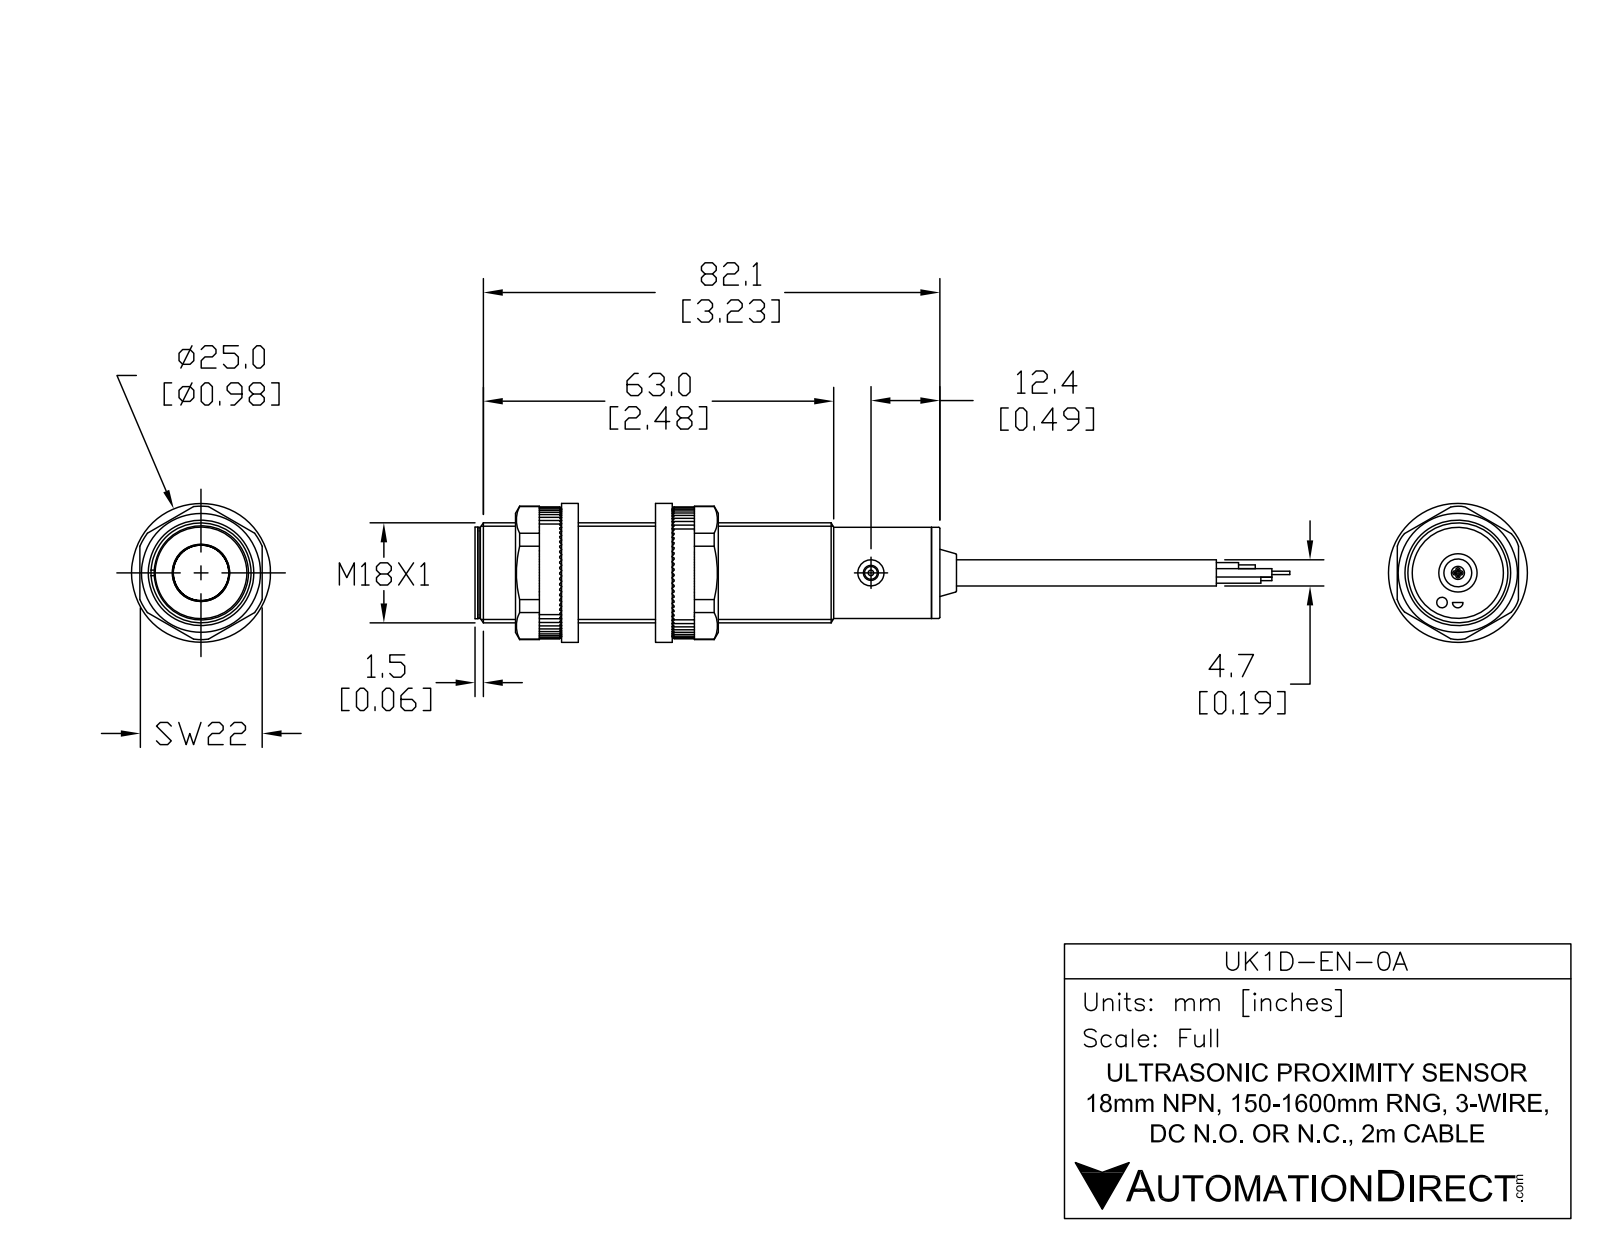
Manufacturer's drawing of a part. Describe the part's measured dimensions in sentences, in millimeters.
The part is named "UK1D-EN-0A". Its 3-D file was written by "SolidWorks 2017 (AUTOMOTIVE_DESIGN)". It is 6 solids with 55 faces: 17 planar, 24 cylindrical and 14 other. Overall it measures 122.7 by 18 by 18 millimeters. Its volume is 21 060 cubic millimeters and its surface area 6 897 square millimeters. Round holes: 2 of diameter 4.7, 1 of diameter 2.7. Round bosses or shafts: 1 of diameter 18, 1 of diameter 16.4, 1 of diameter 15.8, 1 of diameter 9.5, 1 of diameter 4.8, 1 of diameter 2.3. The main face-to-face distances are 81.1, 82.6, 1.5, 1, 82.1, 83.6, 1, 82.1, 83.6, 82.7.
